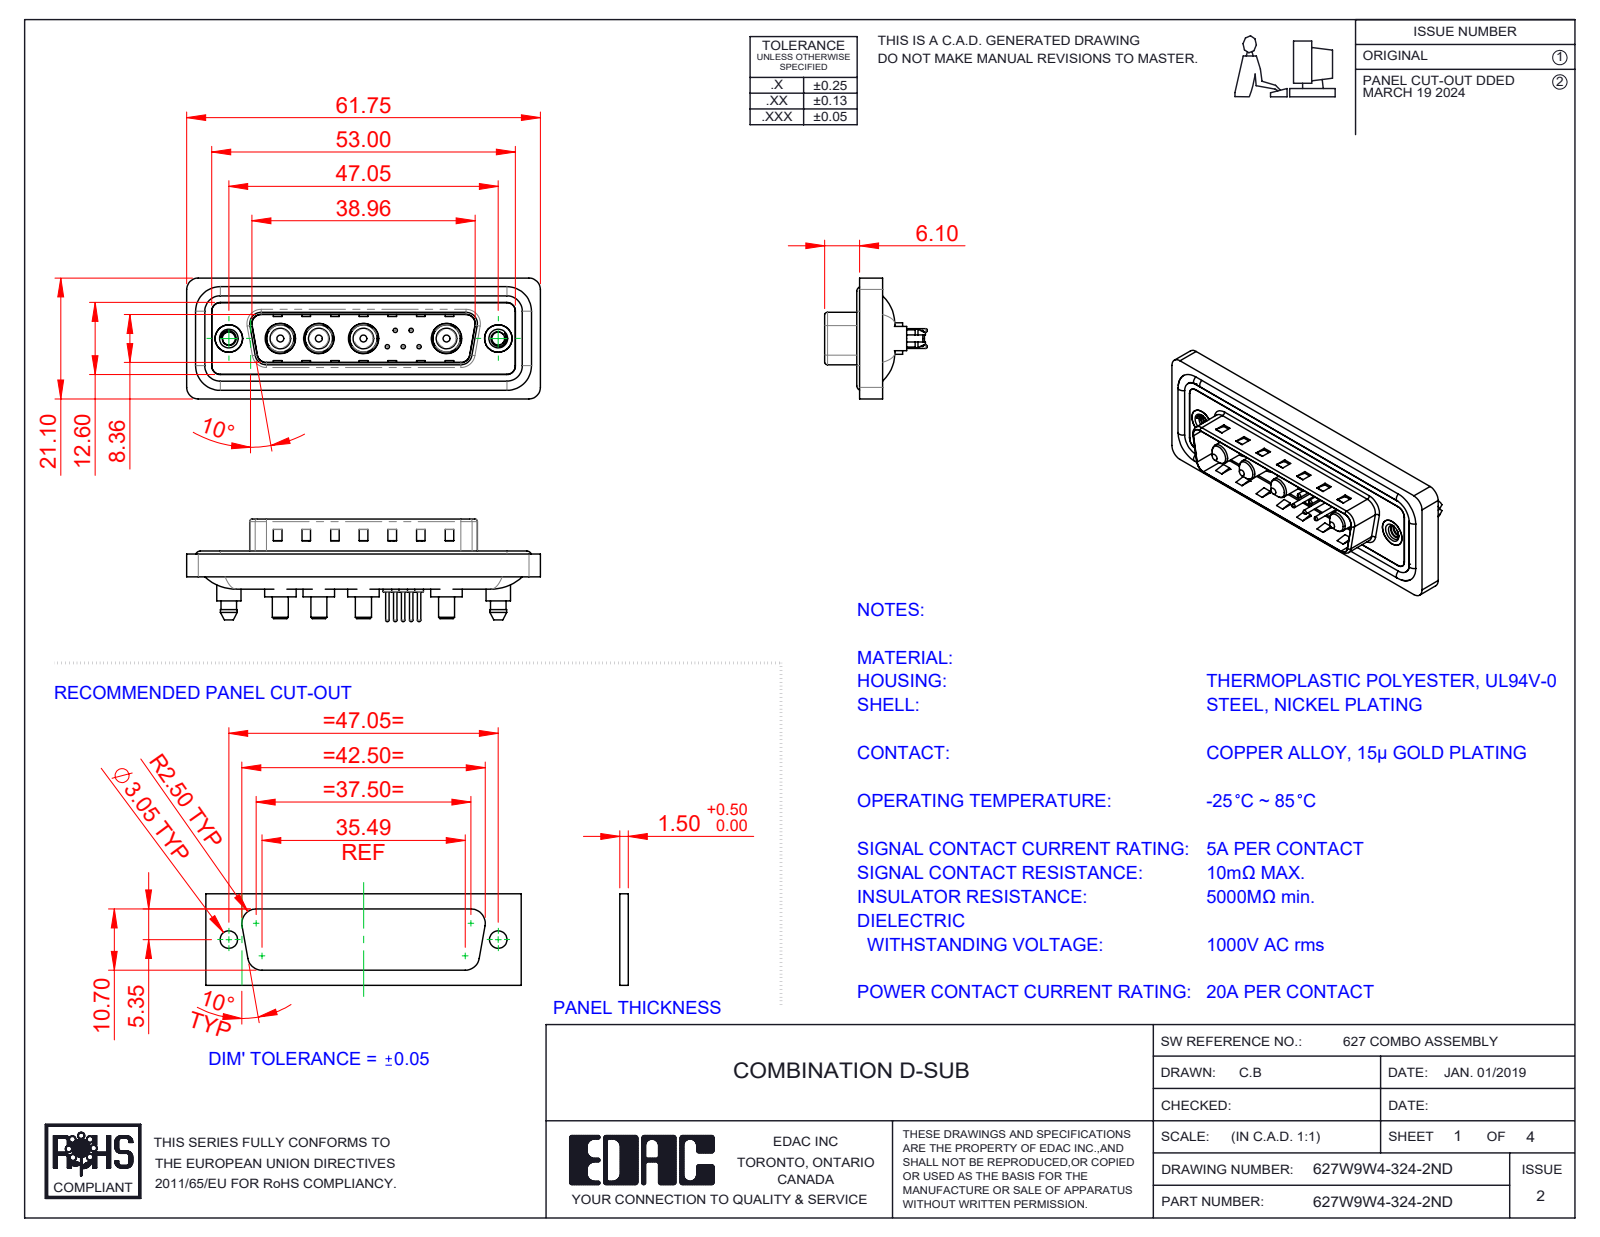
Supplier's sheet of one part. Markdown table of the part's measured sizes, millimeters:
| quantity | value |
| --- | --- |
| part name | 627Combo Contact Row 2_24; 627Combo Housing_9W4; 627Combo Threaded Boardlock_5; 627Combo Shell Front_25 Contacts (+6 more) |
| STEP written by | SolidWorks 2023 (CONFIG_CONTROL_DESIGN) |
| units | millimeters |
| bodies | 20 solids, 882 faces (300 planar, 374 cylindrical, 208 other) |
| overall size | 61.75 × 21.1 × 17.9 |
| volume | 7 539 mm³ |
| surface area | 12 172 mm² |
| round holes (diameter × count) | 0.75 × 5, 1.6 × 5, 2 × 5, 4.85 × 4, 5.3 × 4, 2.26 × 2, 4 × 2, 4.8 × 2, 5 × 2 |
| round bosses / shafts (diameter × count) | 1.5 × 5, 0.6 × 5, 5.5 × 4, 5.2 × 4, 4.75 × 4, 3.75 × 4, 3.6 × 4, 2.8 × 4 |
| partial cylindrical surfaces (radius × count) | 1.5 × 24, 2 × 18, 1.6 × 10, 0.5 × 8, 0.25 × 4, 0.6 × 4, 0.65 × 4, 0.9 × 4 |
| main face-to-face distances | 0.4, 1.5, 1.1, 0.5, 3.1, 1.6, 2.9, 0.82, 9.58, 5.65 |
| hole center spacings | 3.16, 2.77, 5.04, 14.51, 2.78, 4.4, 4.41, 5 |
